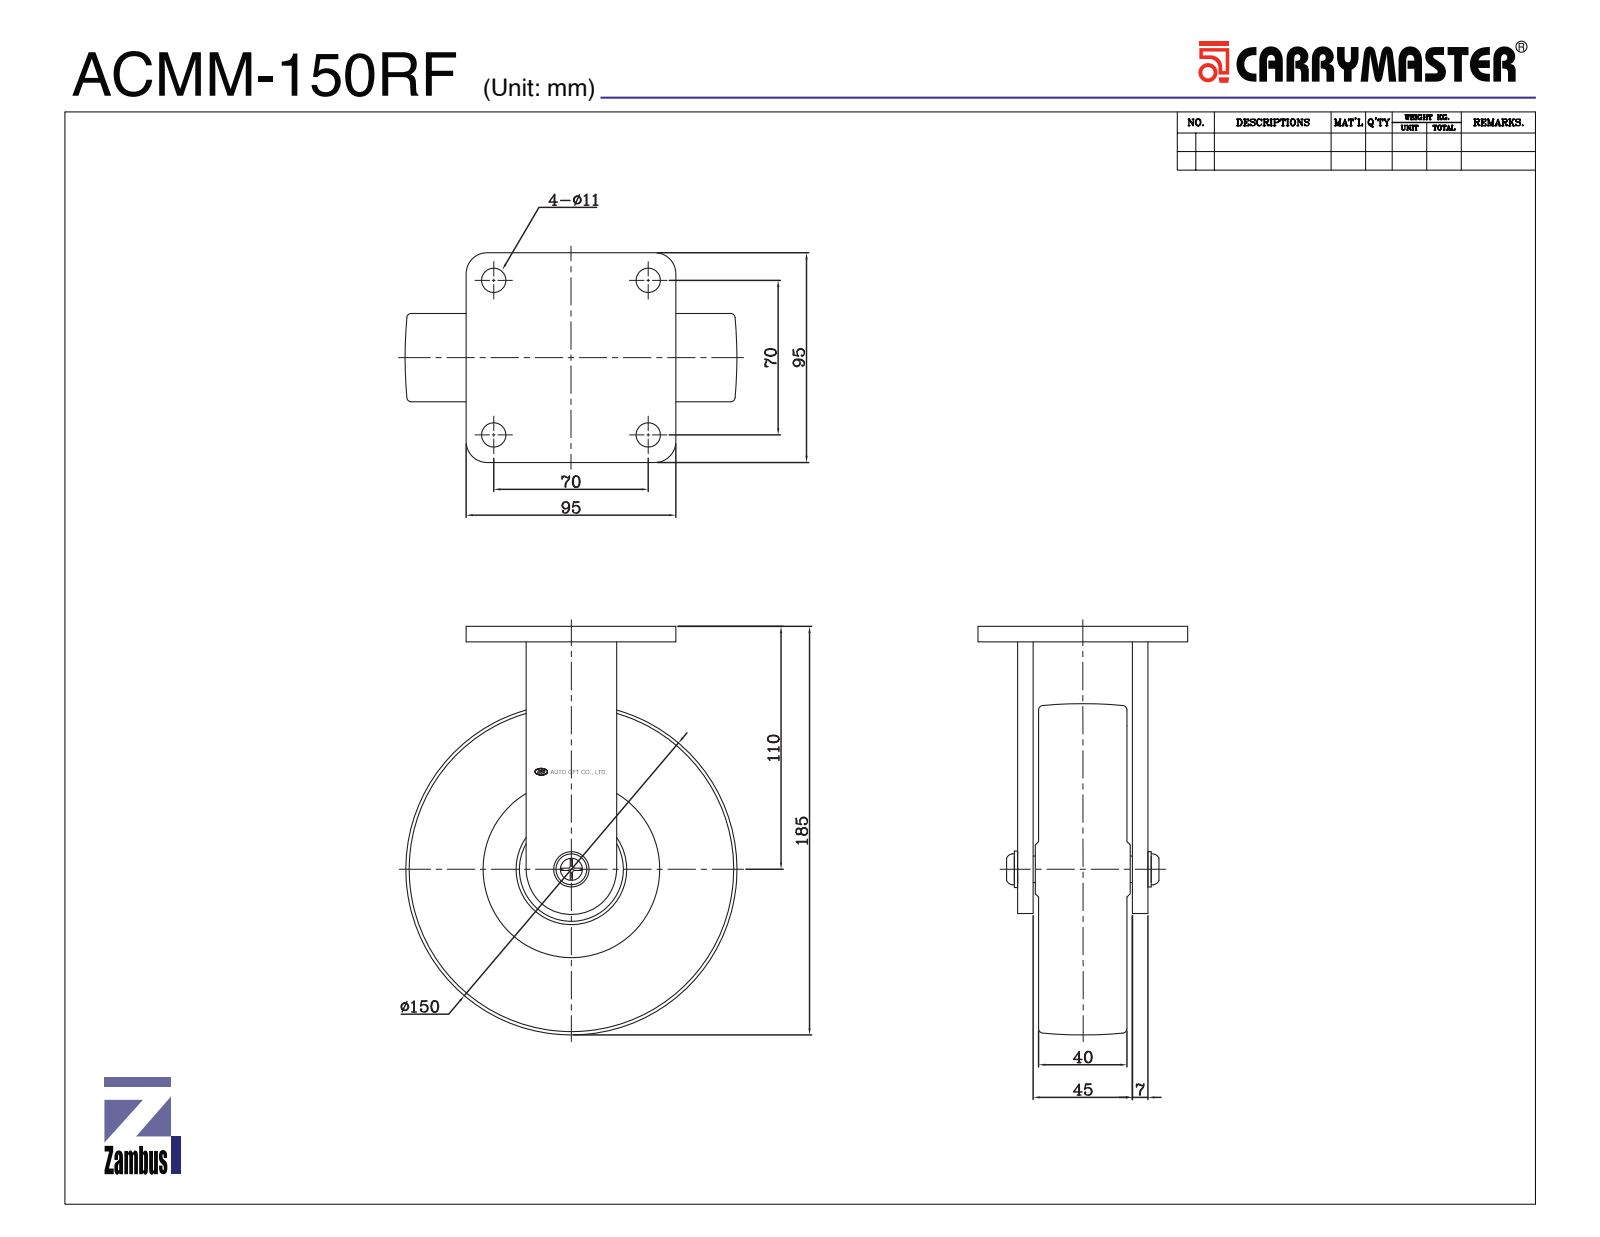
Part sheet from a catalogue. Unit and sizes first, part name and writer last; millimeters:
Units: millimetres
Overall size (bounding box): 185 × 150 × 95
Round holes (diameter × count): ⌀11 ×4, ⌀6.8 ×1, ⌀12.3 ×1, ⌀31.1 ×1, ⌀37 ×1
Round bosses / shafts (diameter × count): ⌀16 ×1, ⌀14 ×1, ⌀12 ×1, ⌀8 ×1
Partial cylindrical surfaces — rounded edges, fillets, slot ends (radius × count): R9.5 ×4, R0.52 ×2, R20.5 ×1
Main face-to-face distances: 7, 40, 9.5, 49.5, 2.5, 52, 42.5, 59, 45, 51
Hole centre spacings: 70, 98.99
Volume: 799 476 mm³ · Surface area: 104 969 mm²
Bodies: 6 solids, 721 faces (202 planar, 57 cylindrical, 462 other)
Part name (STEP PRODUCT): ACMM-150RF
STEP written by: SolidWorks 2015 (CONFIG_CONTROL_DESIGN)
